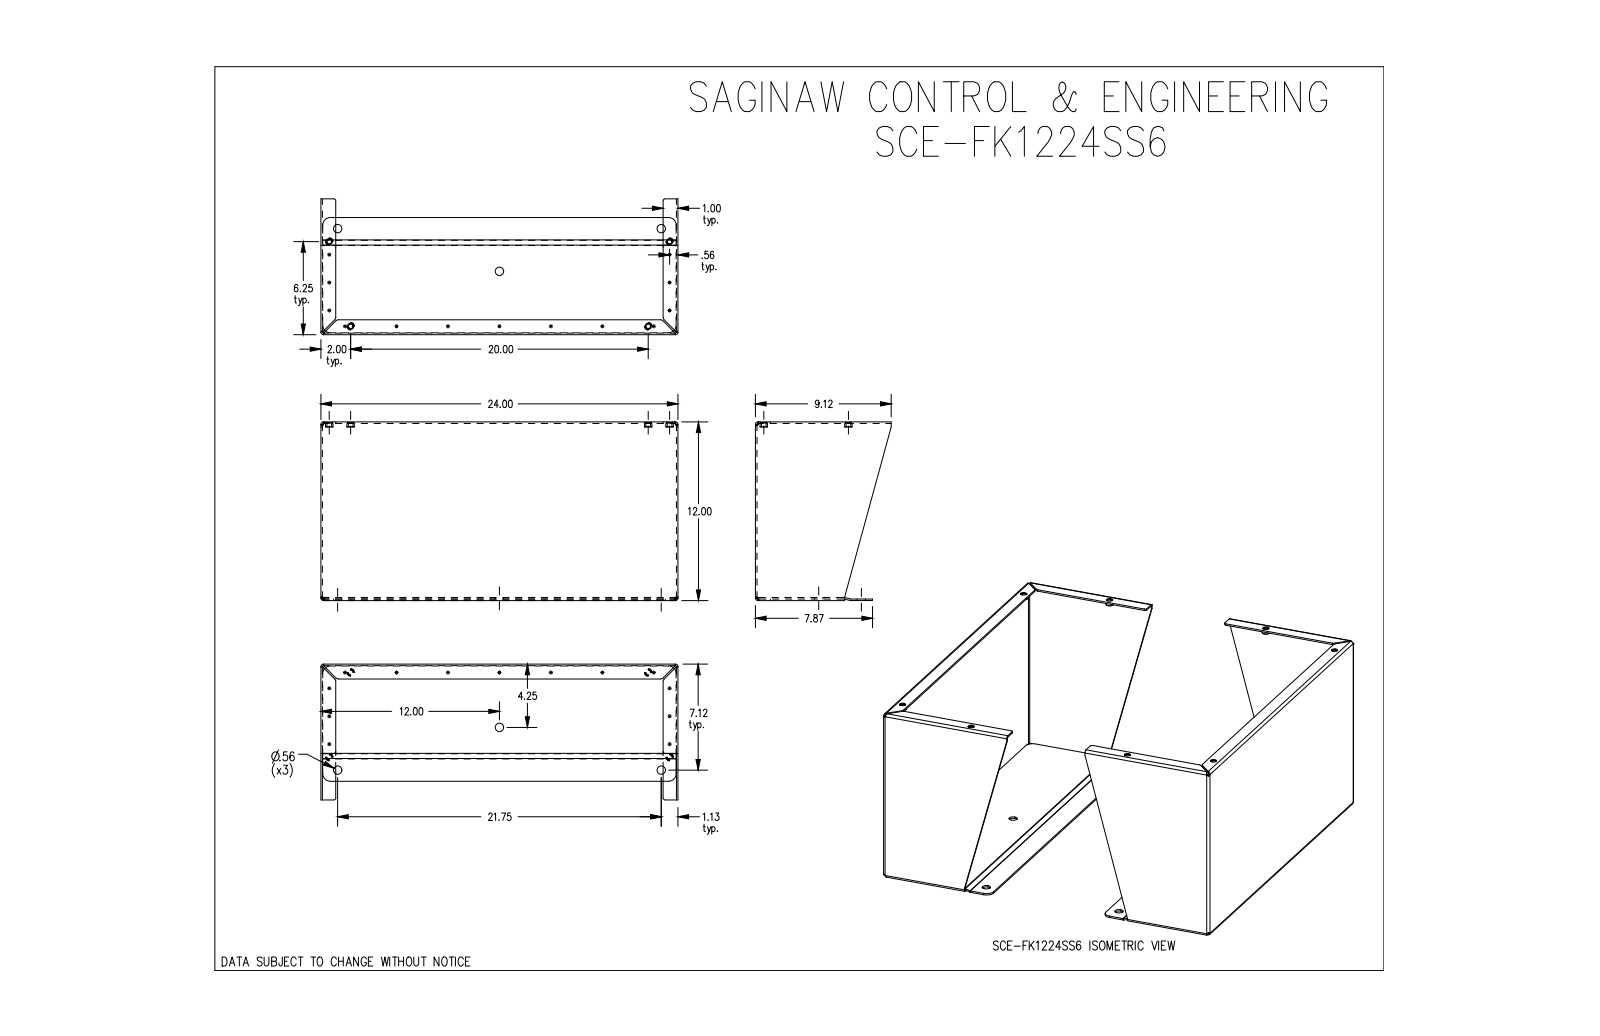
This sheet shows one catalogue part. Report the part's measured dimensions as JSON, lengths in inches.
{"part_name": "SCE-FK1224SS6", "step_written_by": "SolidWorks 2019 (CONFIG_CONTROL_DESIGN)", "units": "inches", "bodies": {"solids": 12, "faces": 286, "planar": 120, "cylindrical": 110, "other": 56}, "overall_size": [24, 24, 12], "volume_in3": 148, "surface_area_in2": 2887, "round_holes": [[0.312, 8], [0.413, 8], [0.563, 6]], "round_bosses_or_shafts": [[0.5, 8], [0.412, 8]], "partial_cylinders_radius": [[0.166, 16], [0.063, 12], [0.125, 8], [0.22, 8], [0.5, 8], [0.062, 6]], "face_to_face_distances": [0.104, 23.896, 23.792, 24, 0.101, 11.893, 11.792, 11.896, 0.205, 11.789], "hole_center_spacings": [1.035, 5.866, 6.614, 10.646, 10.659, 11.611, 16.343, 17.247]}
